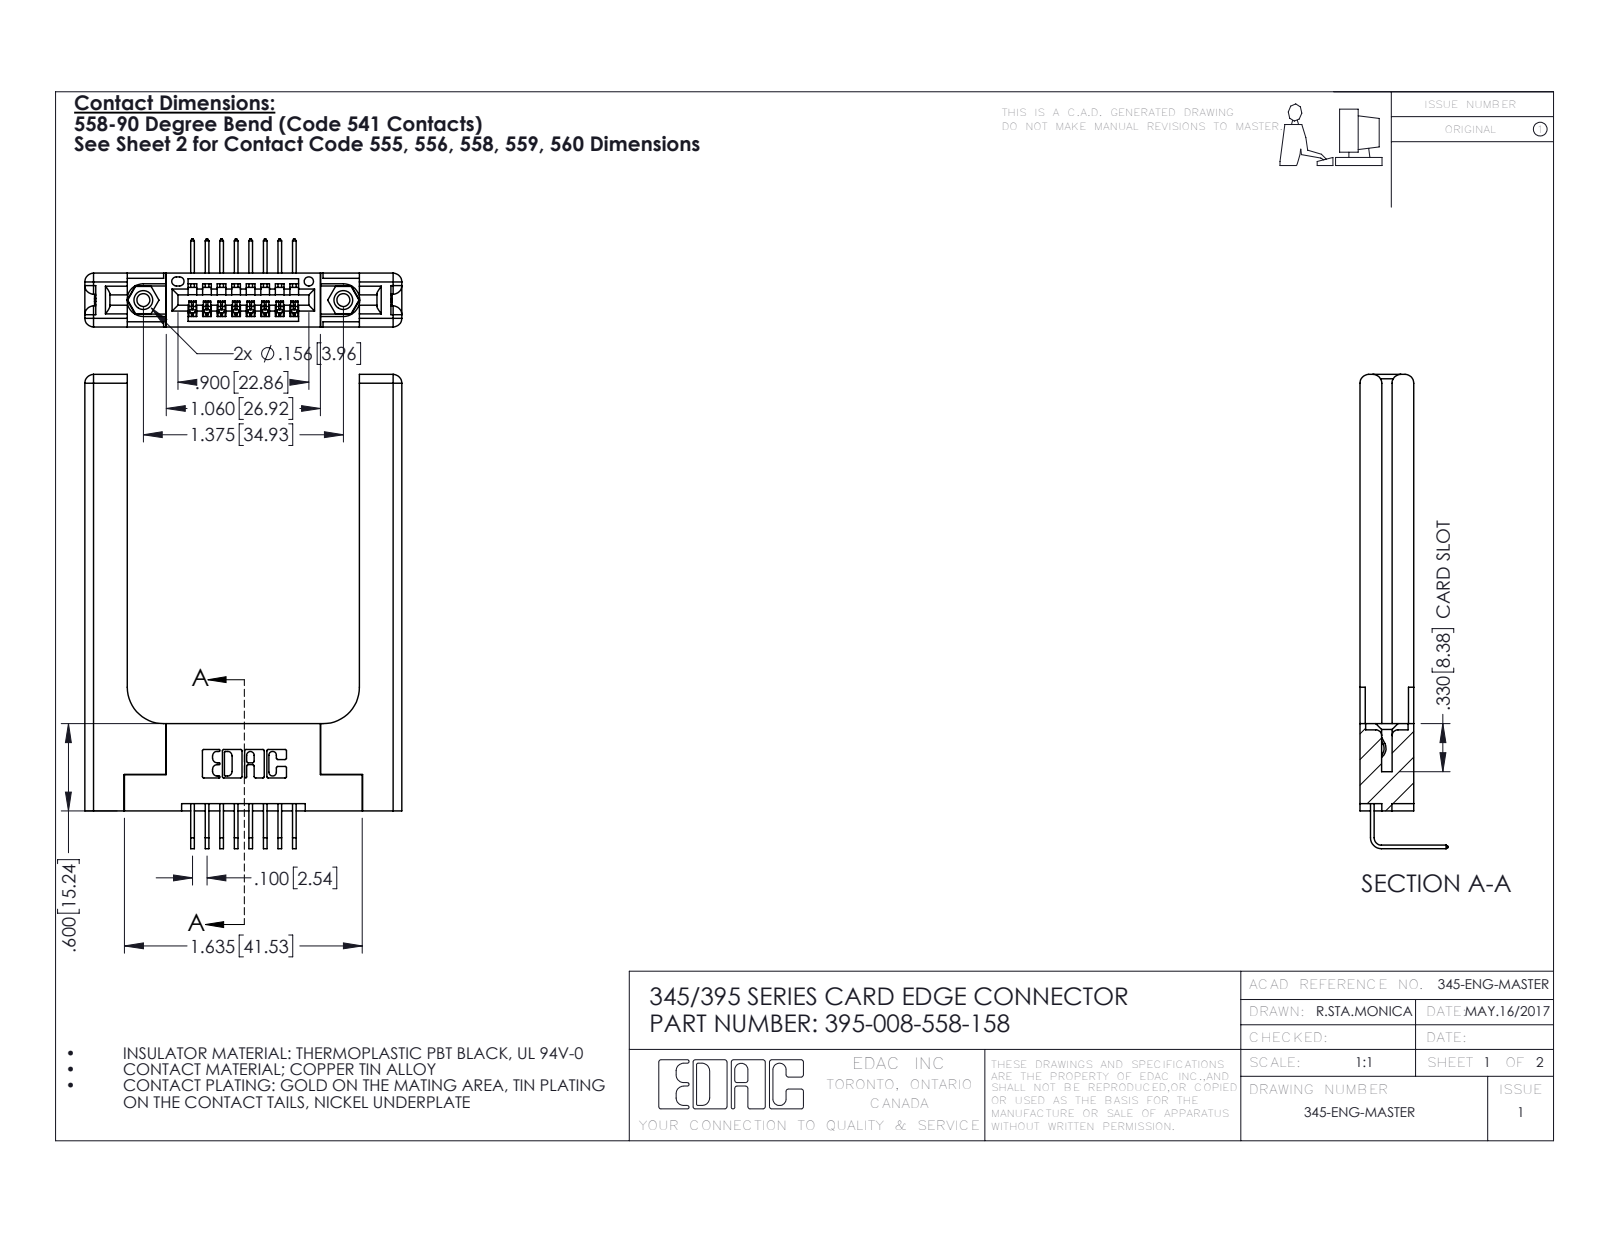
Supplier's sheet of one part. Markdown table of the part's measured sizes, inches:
| quantity | value |
| --- | --- |
| part name | 345-292-001_558 Tail - 2; 345-250-001_345-250-001-102; 345-220-058_345-220-058; 395-008-558-158 (+1 more) |
| STEP written by | SolidWorks 2016 (CONFIG_CONTROL_DESIGN) |
| units | inches |
| bodies | 13 solids, 862 faces (564 planar, 238 cylindrical, 60 other) |
| overall size | 3.259 × 2.179 × 0.605 |
| volume | 0.824 in³ |
| surface area | 18.06 in² |
| round holes (diameter × count) | 0.089 × 2, 0.125 × 2, 0.156 × 2, 0.064 × 1 |
| round bosses / shafts (diameter × count) | 0.155 × 2 |
| partial cylindrical surfaces (radius × count) | 0.01 × 22, 0.006 × 16, 0.06 × 16, 0.007 × 6, 0.031 × 6, 0.026 × 3, 0.03 × 2, 0.031 × 2 |
| main face-to-face distances | 0.37, 0.15, 0.22, 0.072, 0.077, 0.148, 0.298, 1.596, 0.2, 0.071 |
| hole center spacings | 0.27, 1.144, 1.375 |
